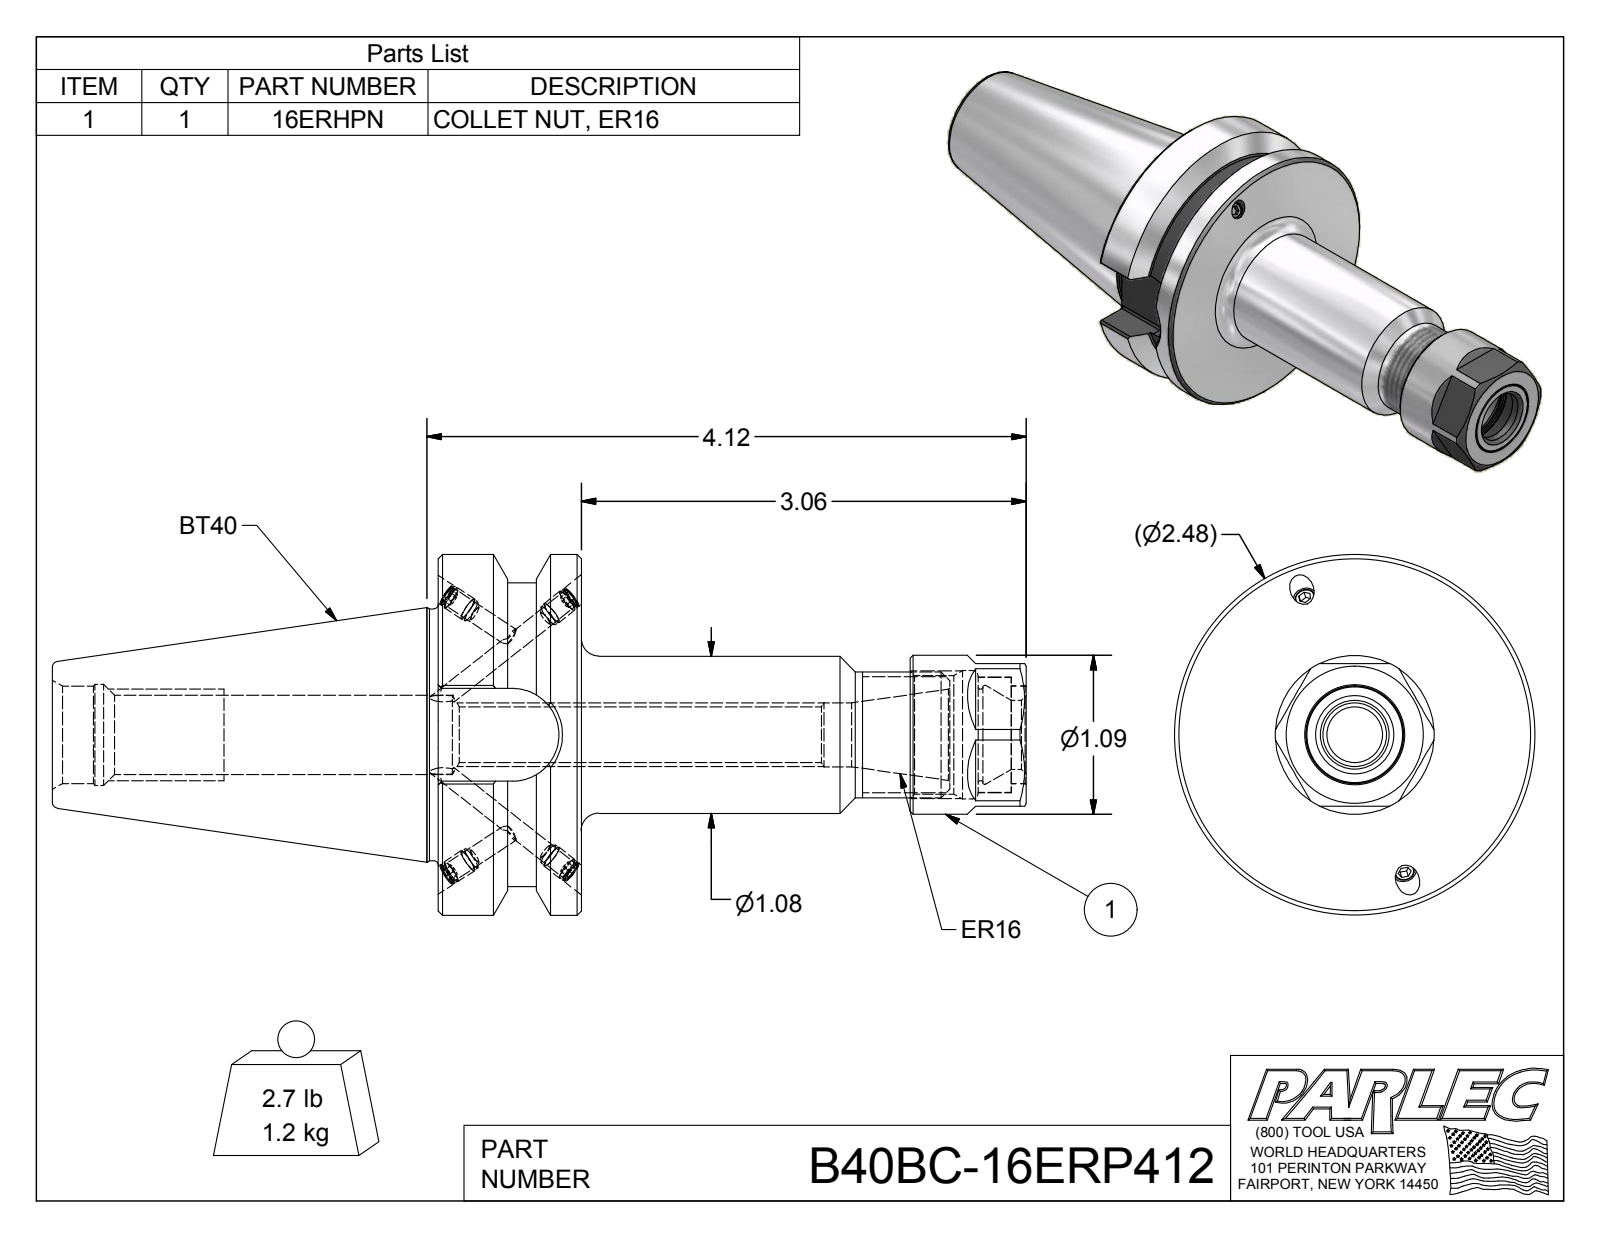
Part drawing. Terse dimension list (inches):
name: B40BC-16ERP412; B40BCB-16ER4-1; 029-965; 16ERHPN
written by: Autodesk Inventor 2012 (AUTOMOTIVE_DESIGN)
unit: in
bodies: 7 solids, 194 faces (87 planar, 53 cylindrical, 54 other)
size: 6.695 × 2.48 × 2.48
volume: 9.437 in³; area: 54.86 in²
holes: 4× ⌀0.13, 4× ⌀0.161, 1× ⌀0.383, 1× ⌀0.44, 1× ⌀0.474, 1× ⌀0.545, 1× ⌀0.63, 1× ⌀0.67, 1× ⌀0.674, 1× ⌀0.68, 1× ⌀0.694, 1× ⌀0.794
bosses: 4× ⌀0.165, 4× ⌀0.157, 1× ⌀2.48, 1× ⌀2.087, 1× ⌀1.73, 1× ⌀1.092, 1× ⌀1.08, 1× ⌀0.866
rounds: 8× R0.02, 1× R0.319
face distances: 0.984, 0.98, 1.78, 4.042, 3.058, 0.172, 0.809, 3.246, 2.262, 0.796
